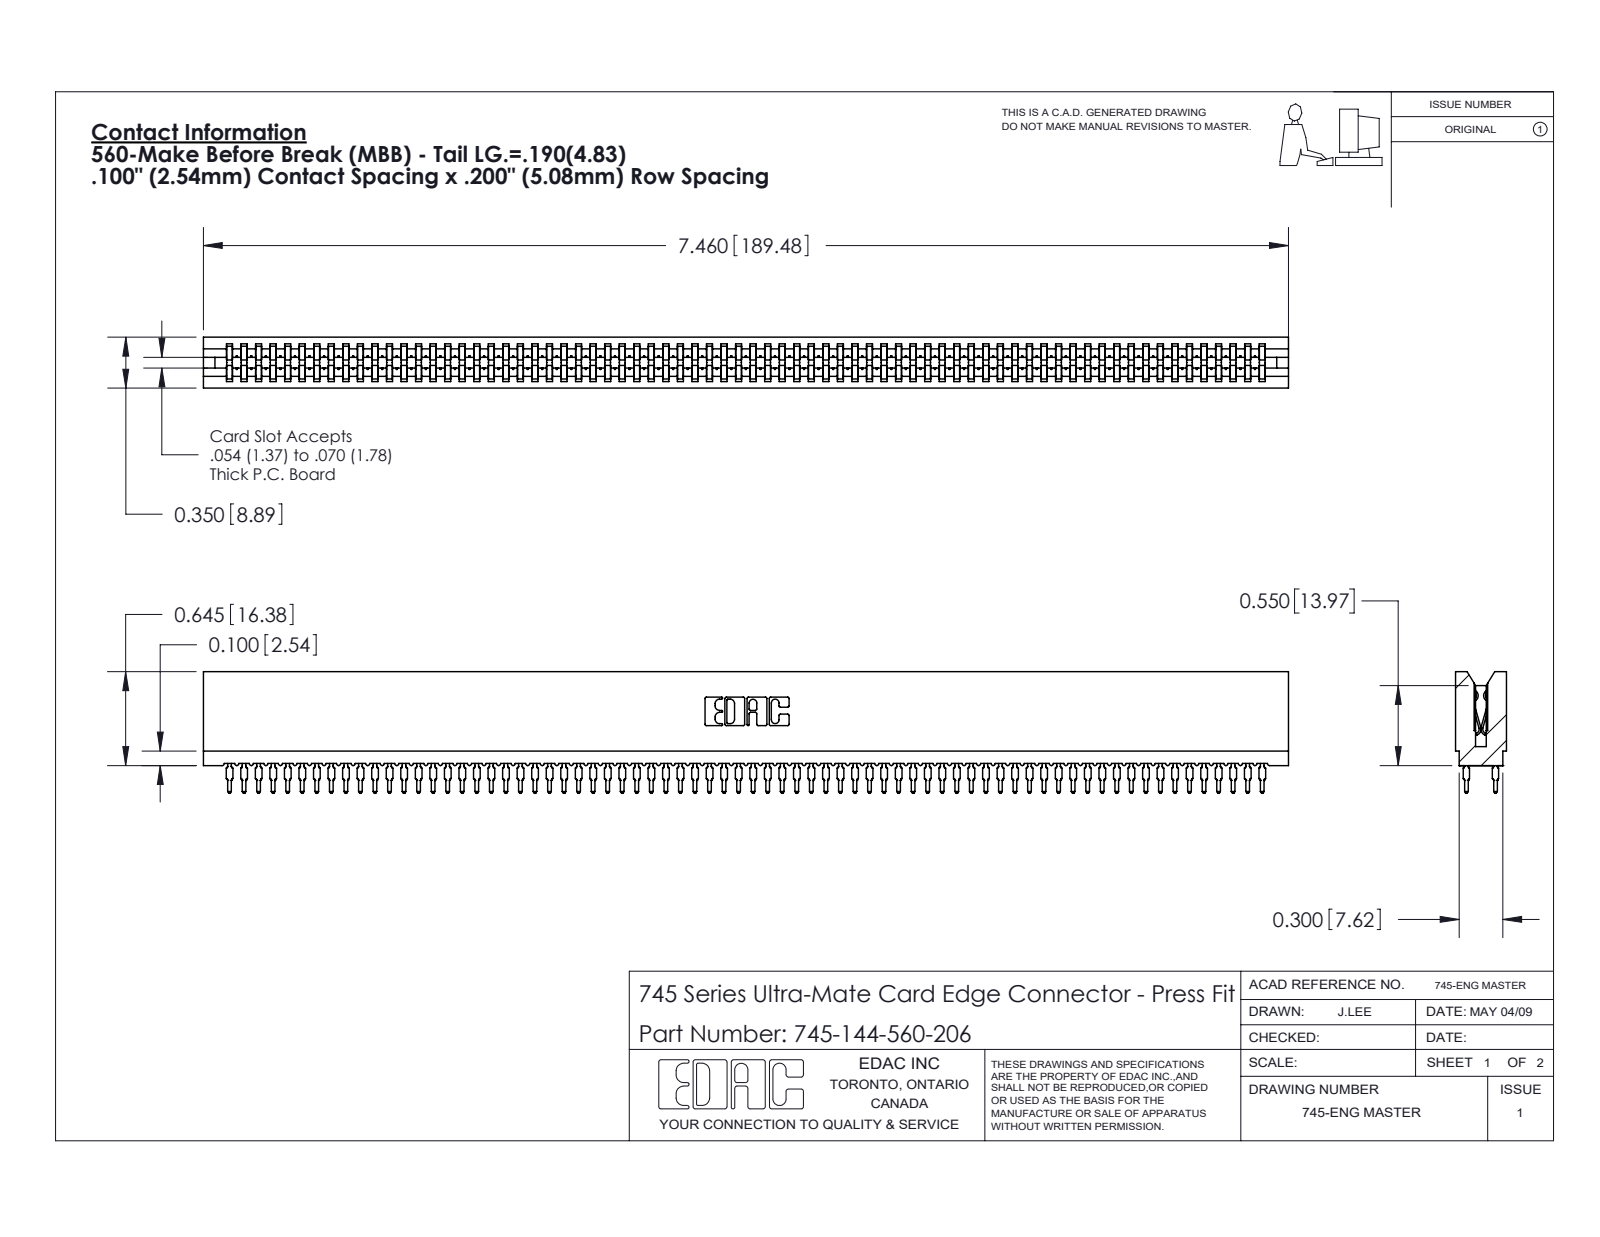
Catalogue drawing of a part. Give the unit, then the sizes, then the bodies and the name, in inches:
Units: inches
Overall size (bounding box): 7.46 × 0.836 × 0.35
Partial cylindrical surfaces — rounded edges, fillets, slot ends (radius × count): R0.021 ×288, R0.015 ×144, R0.01 ×22, R0.005 ×8, R0.011 ×8, R0.007 ×6, R0.031 ×6, R0.026 ×3
Main face-to-face distances: 0.35, 0.063, 0.287, 0.045, 0.305, 0.018, 0.243, 0.138, 0.212, 0.093
Volume: 1.061 in³ · Surface area: 59.45 in²
Bodies: 145 solids, 14280 faces (7400 planar, 3136 cylindrical, 3744 other)
Part name (STEP PRODUCT): 745 Part_Insulator Option - 06; 745-292-001_560; 745-144-560-206
STEP written by: SolidWorks 2020 (CONFIG_CONTROL_DESIGN)
